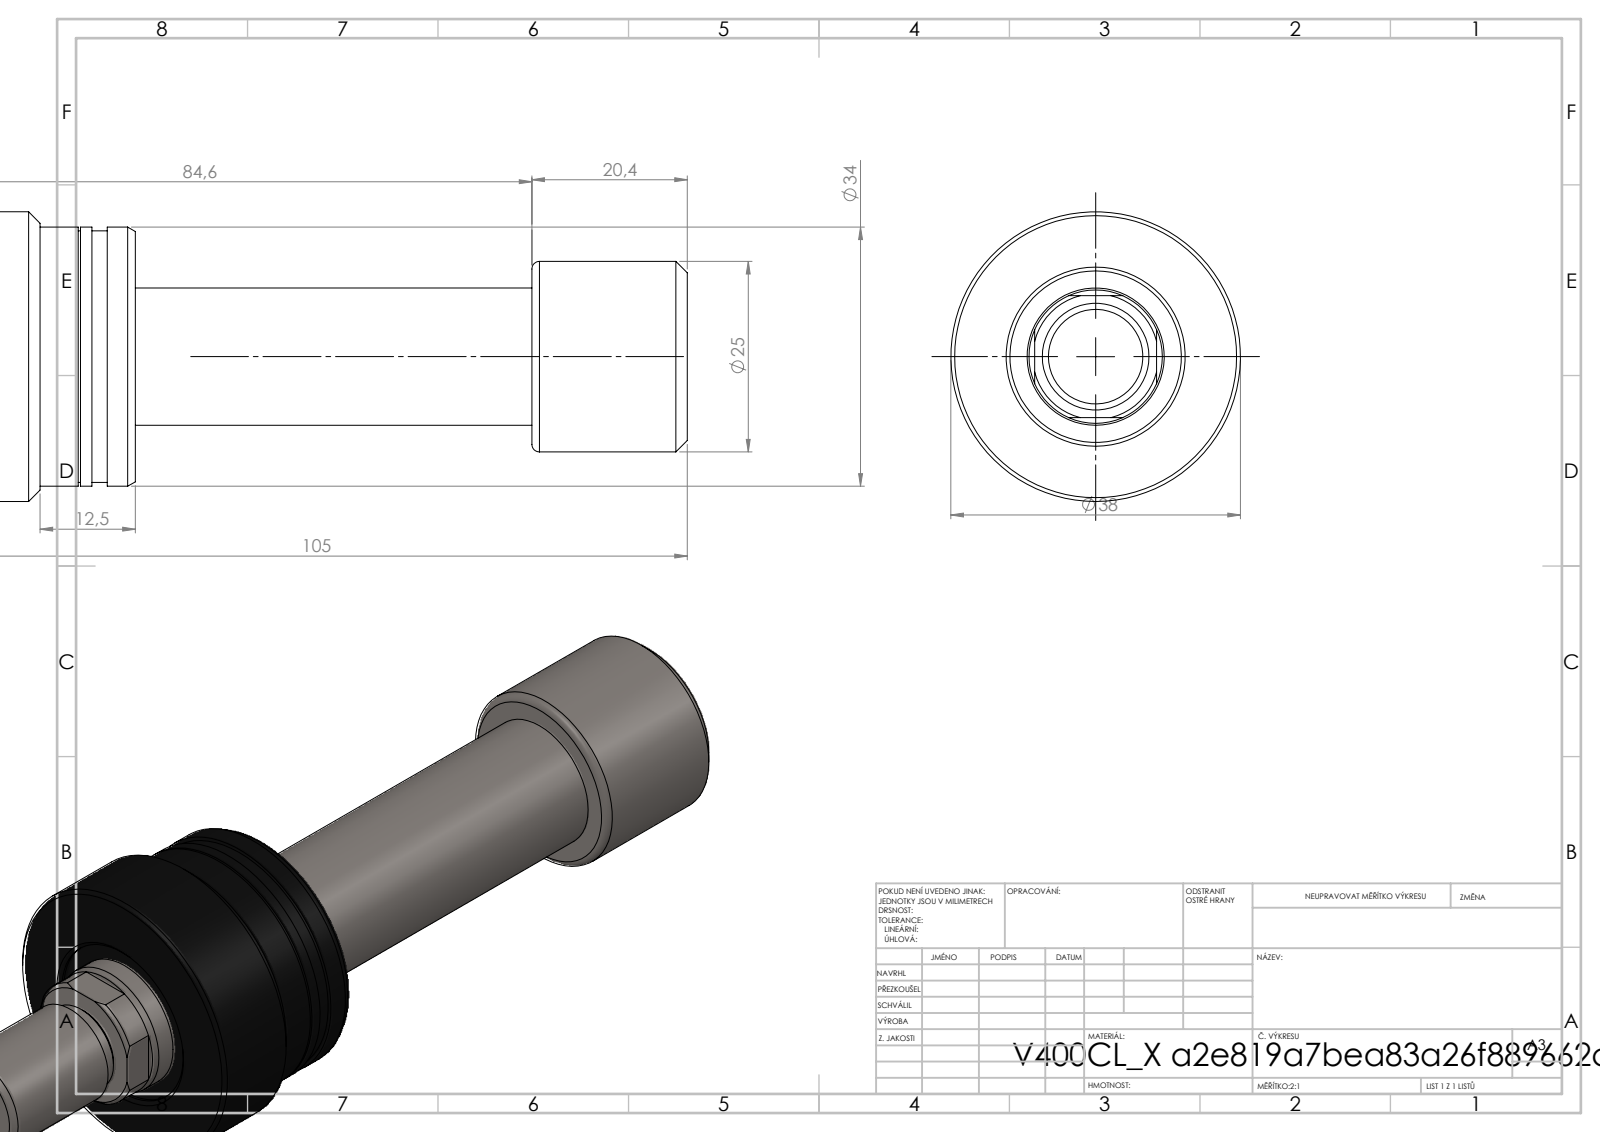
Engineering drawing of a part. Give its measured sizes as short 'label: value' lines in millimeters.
name: V400CL_PC_X; V450CM_MALE_METRIC; V400CL_VC_X
written by: SolidWorks 2019 (CONFIG_CONTROL_DESIGN)
unit: mm
bodies: 3 solids, 93 faces (23 planar, 36 cylindrical, 34 other)
size: 125 × 38 × 38
volume: 52 955 mm³; area: 14 844 mm²
holes: 1× ⌀2.05, 1× ⌀5, 1× ⌀6, 1× ⌀18, 1× ⌀22.5
bosses: 1× ⌀38, 1× ⌀34, 1× ⌀33, 1× ⌀25, 1× ⌀14, 1× ⌀12, 1× ⌀11
rounds: 1× R8.75
face distances: 72.45, 105, 32.55, 20.4, 52.05, 84.6, 97.45, 77.05, 25, 7.55
